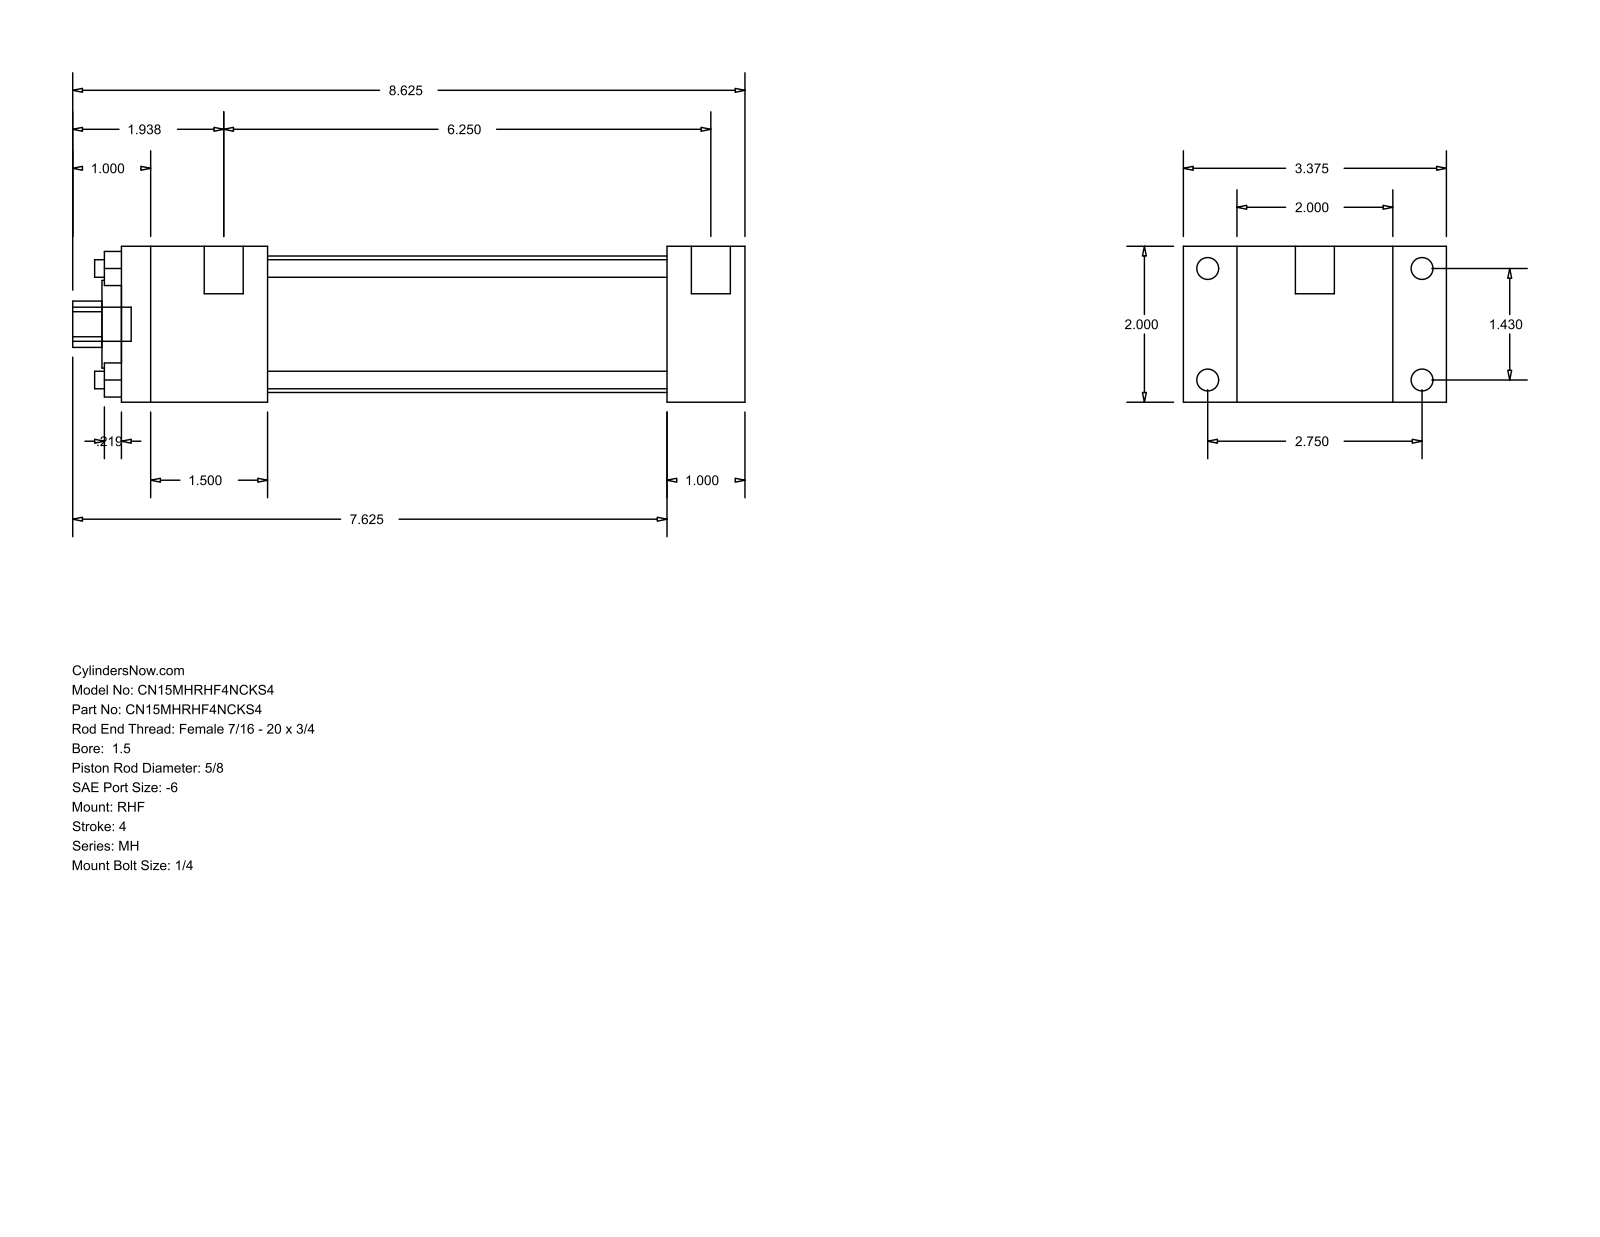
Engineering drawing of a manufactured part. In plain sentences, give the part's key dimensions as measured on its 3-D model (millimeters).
The part is named "MH_RHF__0150_0.625". Its 3-D file was written by "GSSL Pune (CONFIG_CONTROL_DESIGN)". It is 0 solids with 88 faces: 60 planar, 28 cylindrical and 0 other. Overall it measures 219.07 by 85.72 by 50.8 millimeters. Round holes: 4 of diameter 5.71, 1 of diameter 15.88, 1 of diameter 28.57, 1 of diameter 44.45. Round bosses or shafts: 4 of diameter 7.14, 4 of diameter 5.56, 2 of diameter 12.7, 1 of diameter 11.11. Partial cylindrical surfaces (rounded edges, fillets, slot ends): 1 of radius 7.54. The main face-to-face distances are 50.8, 17.46, 68.26, 25.39, 177.8, 203.19, 85.72, 47.62, 130.18, 155.57. The hole center spacings are 25.68, 36.32, 51.36.
